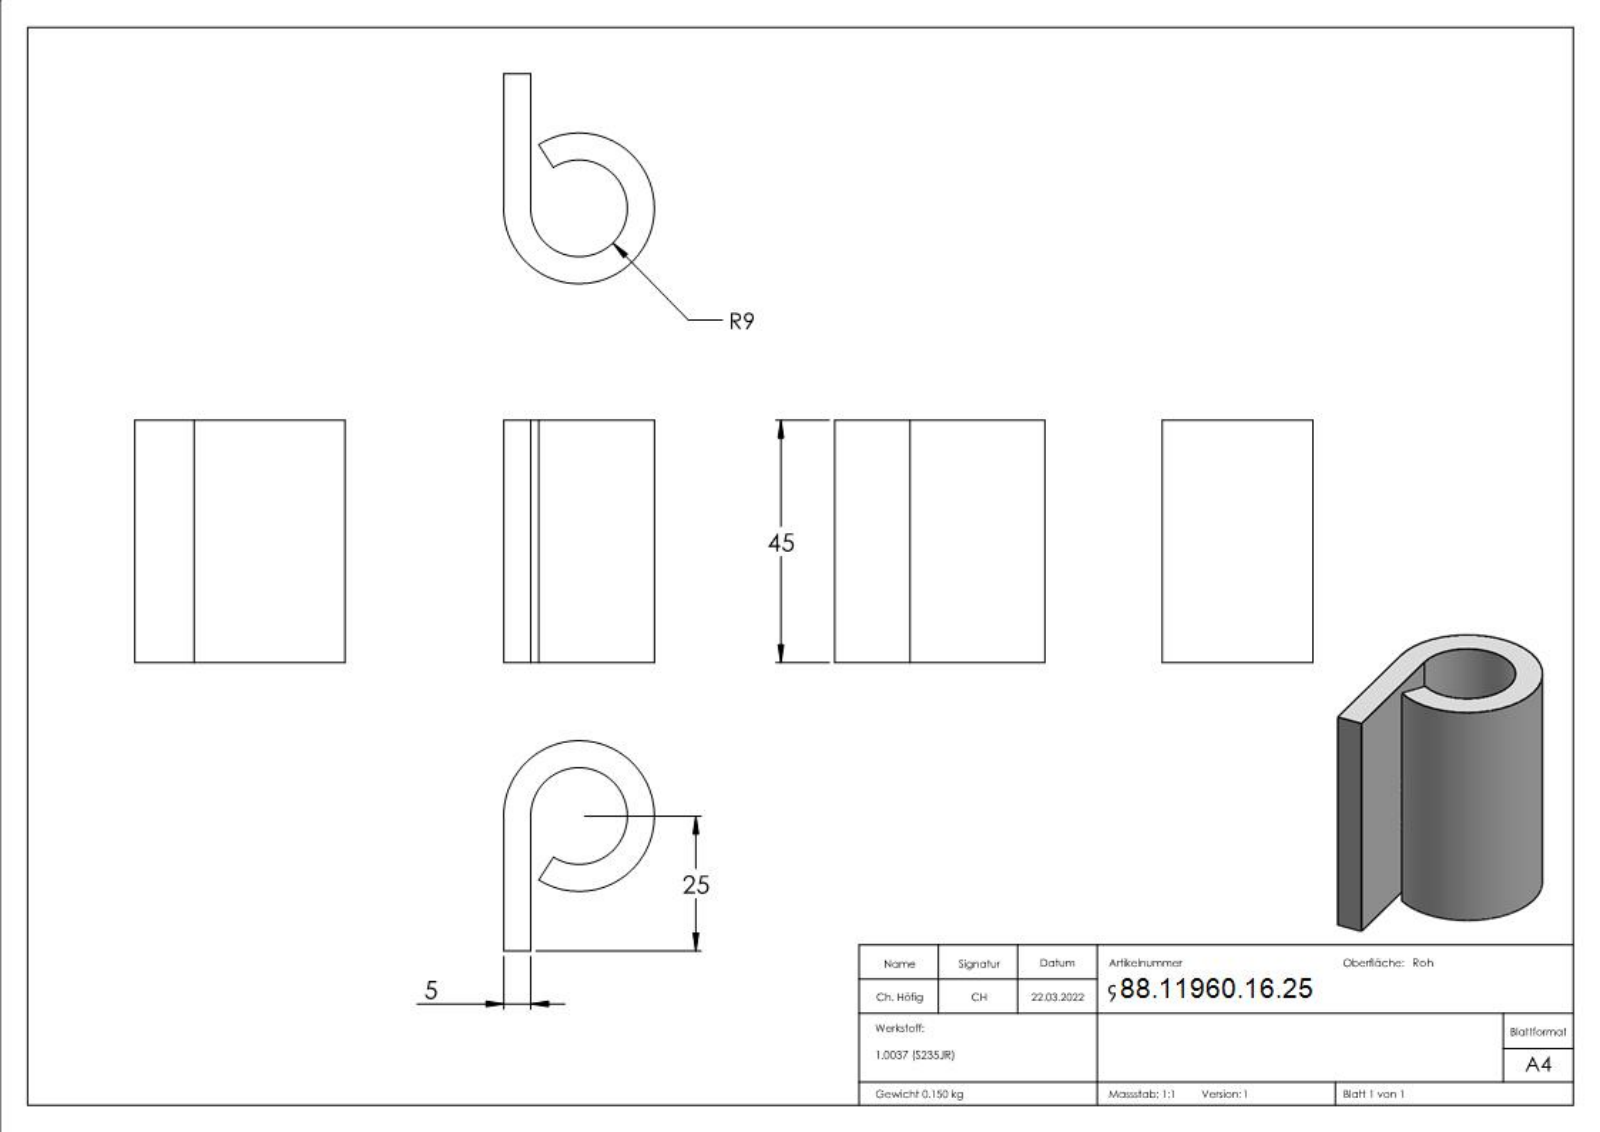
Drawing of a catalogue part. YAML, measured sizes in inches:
part_name: "960-16-25"
step_written_by: "SolidWorks 2018 (CONFIG_CONTROL_DESIGN)"
units: inches
bodies: {solids: 1, faces: 219, planar: 119, cylindrical: 2, other: 98}
overall_size: [1.772, 1.535, 1.102]
volume: 1.177
surface_area: 13.99
round_holes:
  - {diameter: 0.709, count: 1}
round_bosses_or_shafts:
  - {diameter: 1.102, count: 1}
face_to_face_distances: [0.197, 1.772, 0.117, 0.049, 0.065, 0.015, 0.226, 0.08, 0.023, 0.054]
